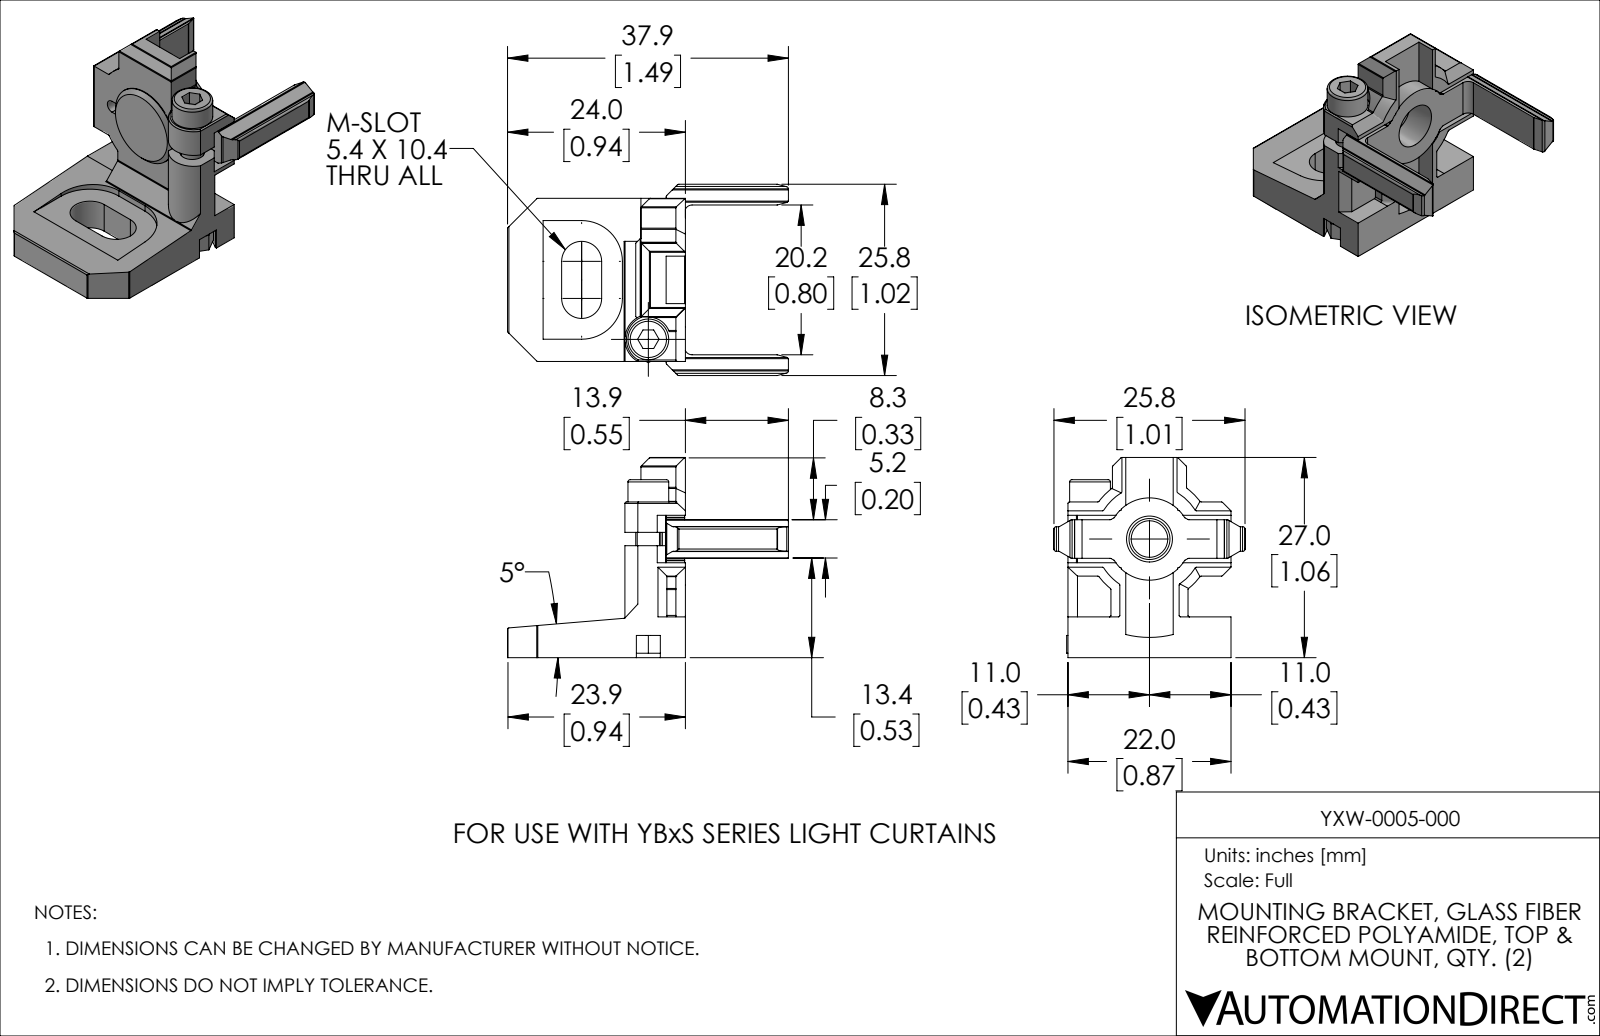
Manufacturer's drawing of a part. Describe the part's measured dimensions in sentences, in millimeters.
The part is named "YXW-0005-000". Its 3-D file was written by "SolidWorks 2019 (AUTOMOTIVE_DESIGN)". It is 2 solids with 312 faces: 167 planar, 125 cylindrical and 20 other. Overall it measures 37.9 by 27 by 25.8 millimeters. Its volume is 4 030 cubic millimeters and its surface area 4 463 square millimeters. Round holes: 1 of diameter 2.5, 1 of diameter 3.3, 1 of diameter 11.1. Round bosses or shafts: 1 of diameter 5.5, 1 of diameter 3. Partial cylindrical surfaces (rounded edges, fillets, slot ends): 60 of radius 0.2, 32 of radius 0.3, 2 of radius 1, 2 of radius 2.7, 2 of radius 4.5, 2 of radius 5.5, 1 of radius 0.2, 1 of radius 0.9. The main face-to-face distances are 4.1, 14.2, 6, 1.8, 5.9, 2.5, 5.8, 2.6, 22, 3.4.
